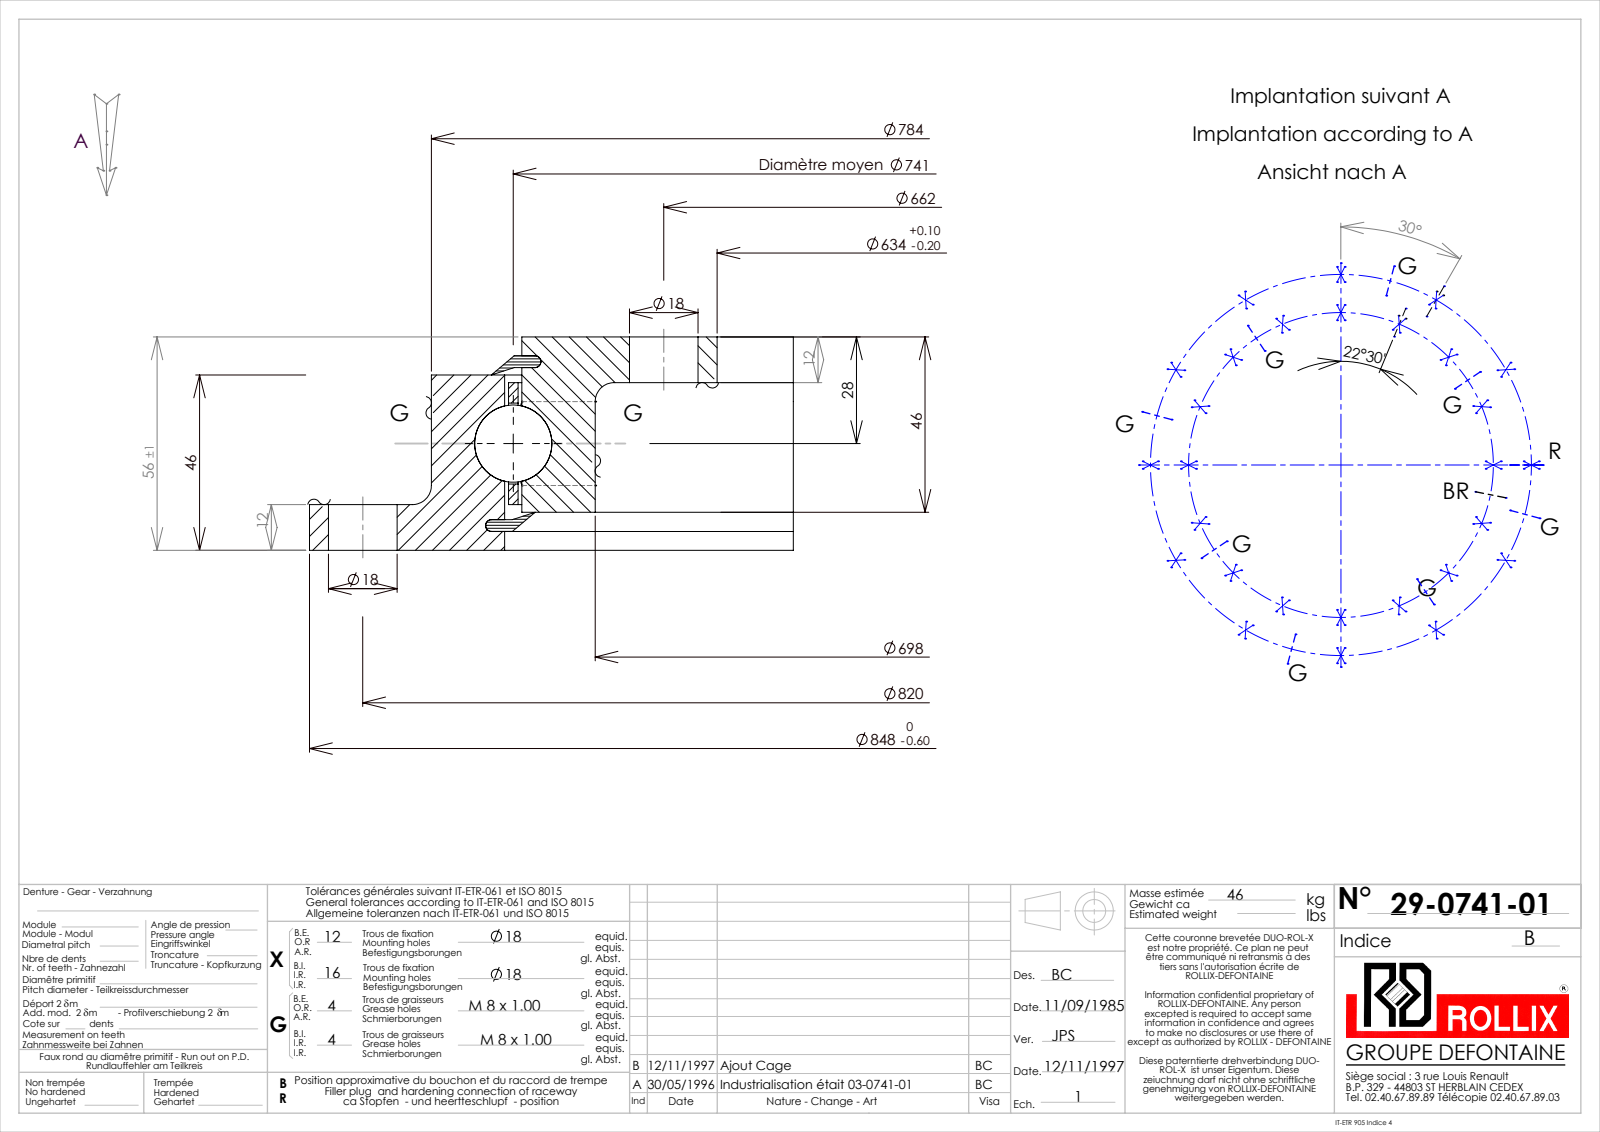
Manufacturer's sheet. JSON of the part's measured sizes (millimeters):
{"part_name": "23-0741-01", "step_written_by": "SolidWorks 2016 (CONFIG_CONTROL_DESIGN)", "units": "millimeters", "bodies": {"solids": 13, "faces": 314, "planar": 94, "cylindrical": 108, "other": 112}, "overall_size": [848, 848, 56], "volume_mm3": 5435000, "surface_area_mm2": 1120000, "round_holes": [[18, 28], [7, 8], [634, 1], [698, 1], [745.5, 1]], "round_bosses_or_shafts": [[8, 8], [848, 1], [784, 1], [736.5, 1]], "face_to_face_distances": [12, 44, 56, 10, 46, 2, 34, 32, 36, 4.95], "hole_center_spacings": [410, 129.15, 331, 468.1, 550.43, 212.23, 253.34, 579.83]}
